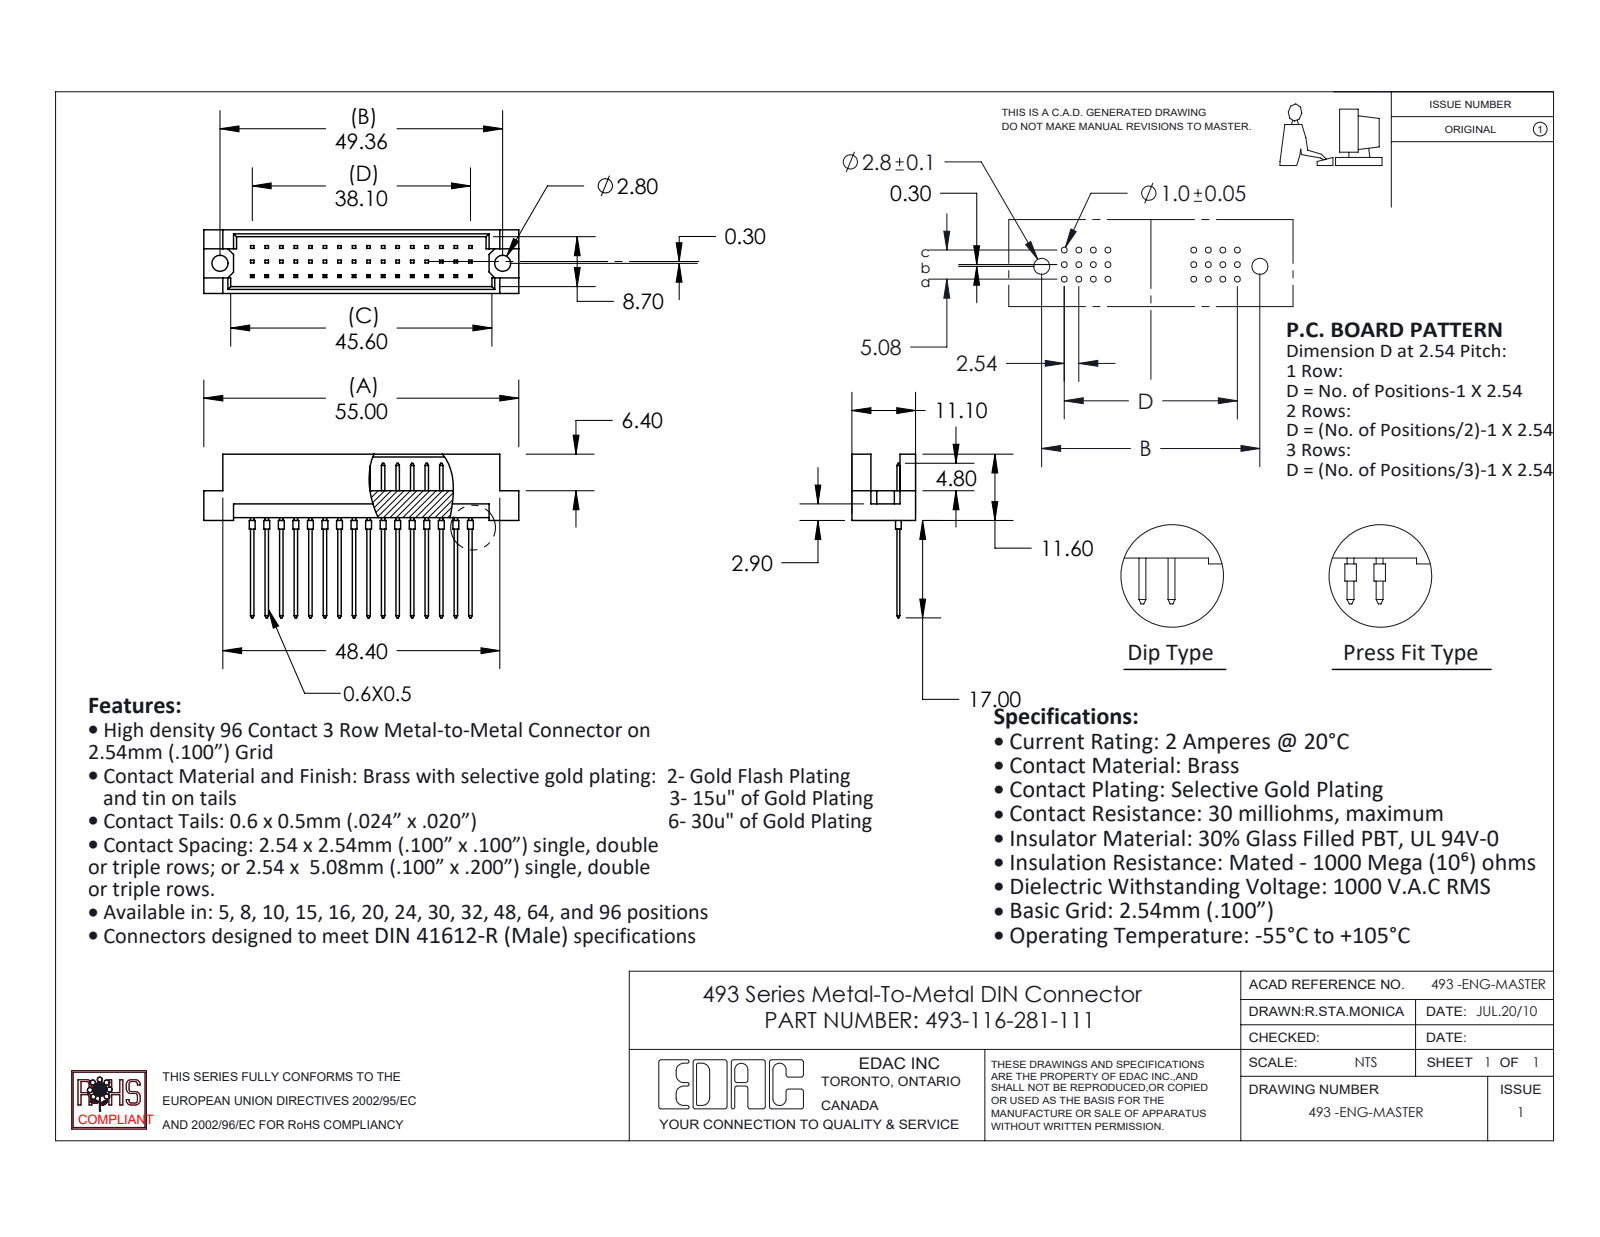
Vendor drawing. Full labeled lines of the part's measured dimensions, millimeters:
Part name (STEP PRODUCT): 493-116-281-111; 493 Part_48; 493-290_81
STEP written by: SolidWorks 2020 (CONFIG_CONTROL_DESIGN)
Units: millimetres
Bodies: 17 solids, 596 faces (560 planar, 36 cylindrical, 0 other)
Overall size (bounding box): 55 × 28.6 × 11.1
Volume: 3 412 mm³ · Surface area: 4 739 mm²
Round holes (diameter × count): ⌀2.8 ×2
Round bosses / shafts (diameter × count): ⌀1 ×16
Main face-to-face distances: 1.2, 9.9, 11.1, 0.5, 2.54, 8.7, 5.08, 4.7, 2.76, 8.34
Hole centre spacings: 49.36
